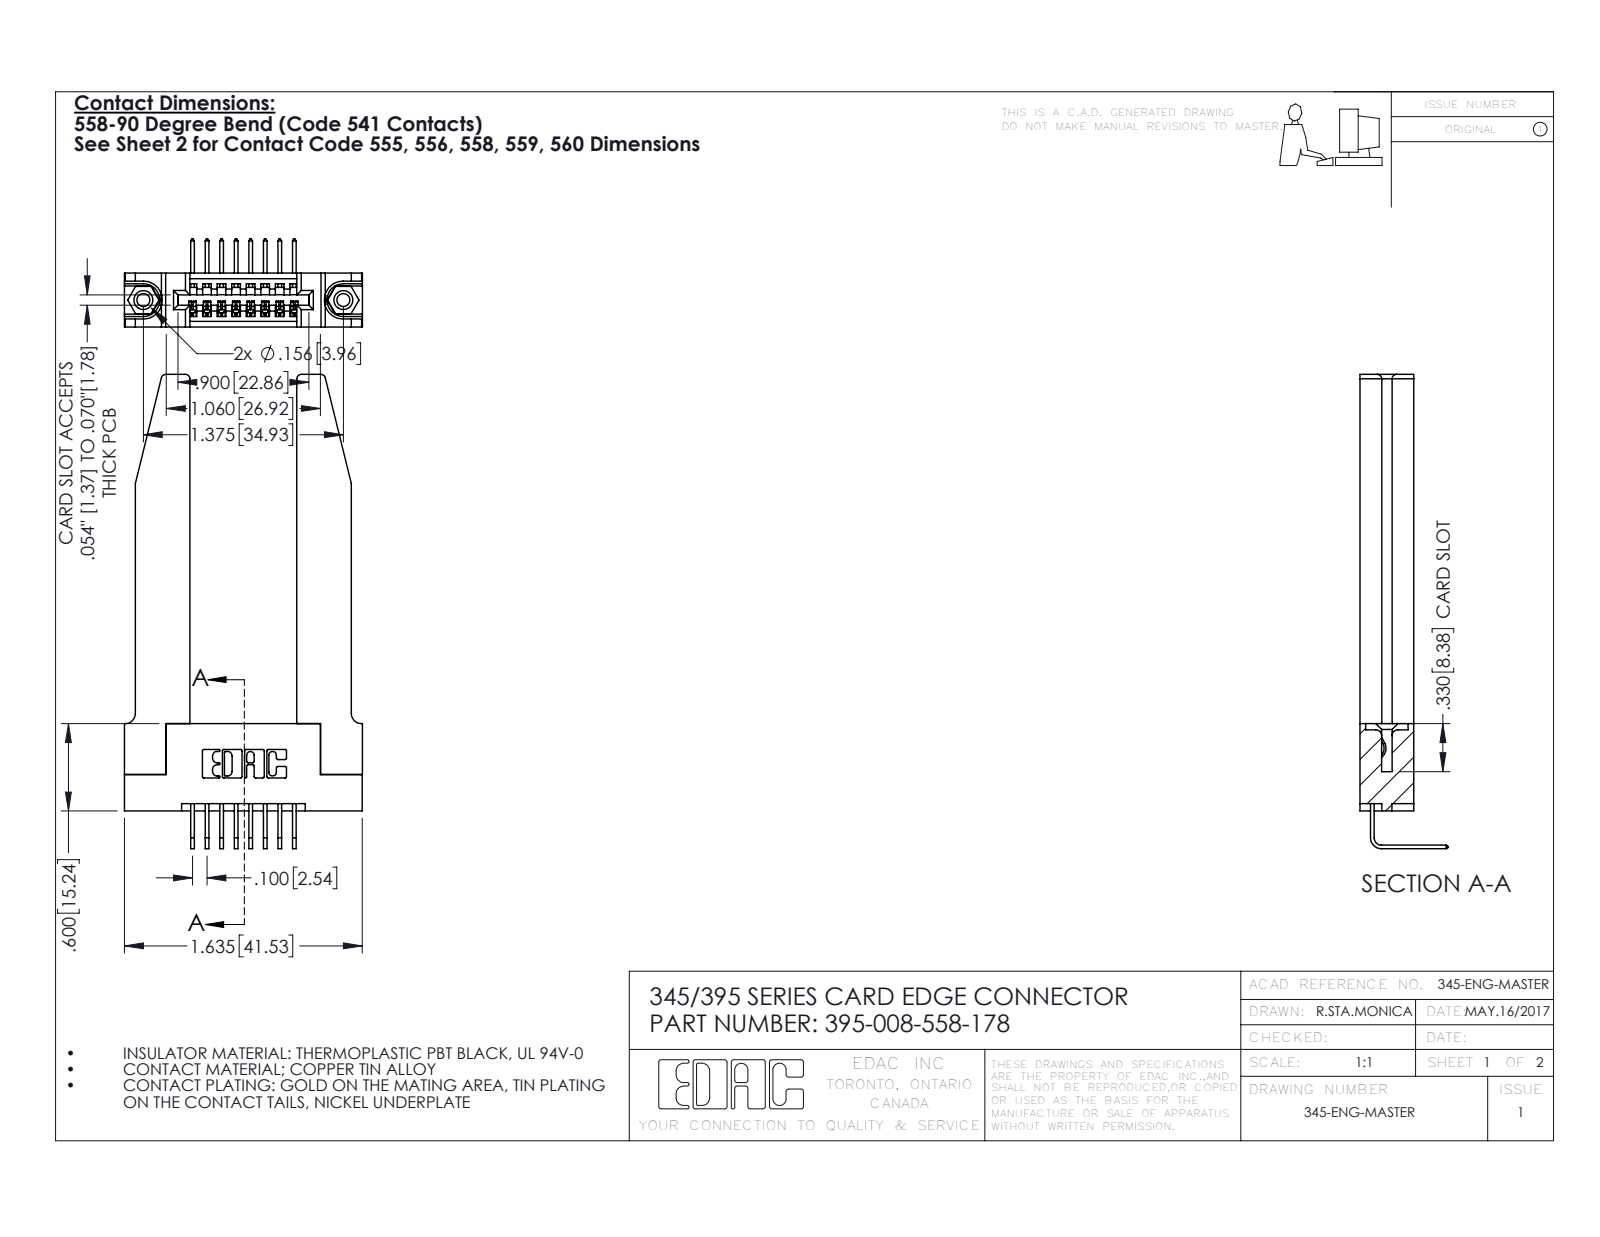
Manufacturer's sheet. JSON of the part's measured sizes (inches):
{"part_name": "345-220-078_345-220-078; 345 Part_Flush Mounting Lugs - 0.156 Dia-TH; 395-008-558-178; 345-292-001_558 Tail - 2 (+1 more)", "step_written_by": "SolidWorks 2016 (CONFIG_CONTROL_DESIGN)", "units": "inches", "bodies": {"solids": 13, "faces": 840, "planar": 558, "cylindrical": 230, "other": 52}, "overall_size": [3.259, 1.636, 0.605], "volume_in3": 0.7, "surface_area_in2": 17.75, "round_holes": [[0.089, 2], [0.125, 2], [0.156, 2], [0.064, 1]], "round_bosses_or_shafts": [[0.155, 2]], "partial_cylinders_radius": [[0.01, 22], [0.006, 16], [0.03, 8], [0.007, 6], [0.031, 6], [0.026, 3], [0.031, 2], [0.04, 2]], "face_to_face_distances": [0.37, 0.15, 0.072, 0.22, 0.148, 0.298, 0.735, 0.077, 0.2, 0.095], "hole_center_spacings": [0.27, 1.144, 1.375]}
